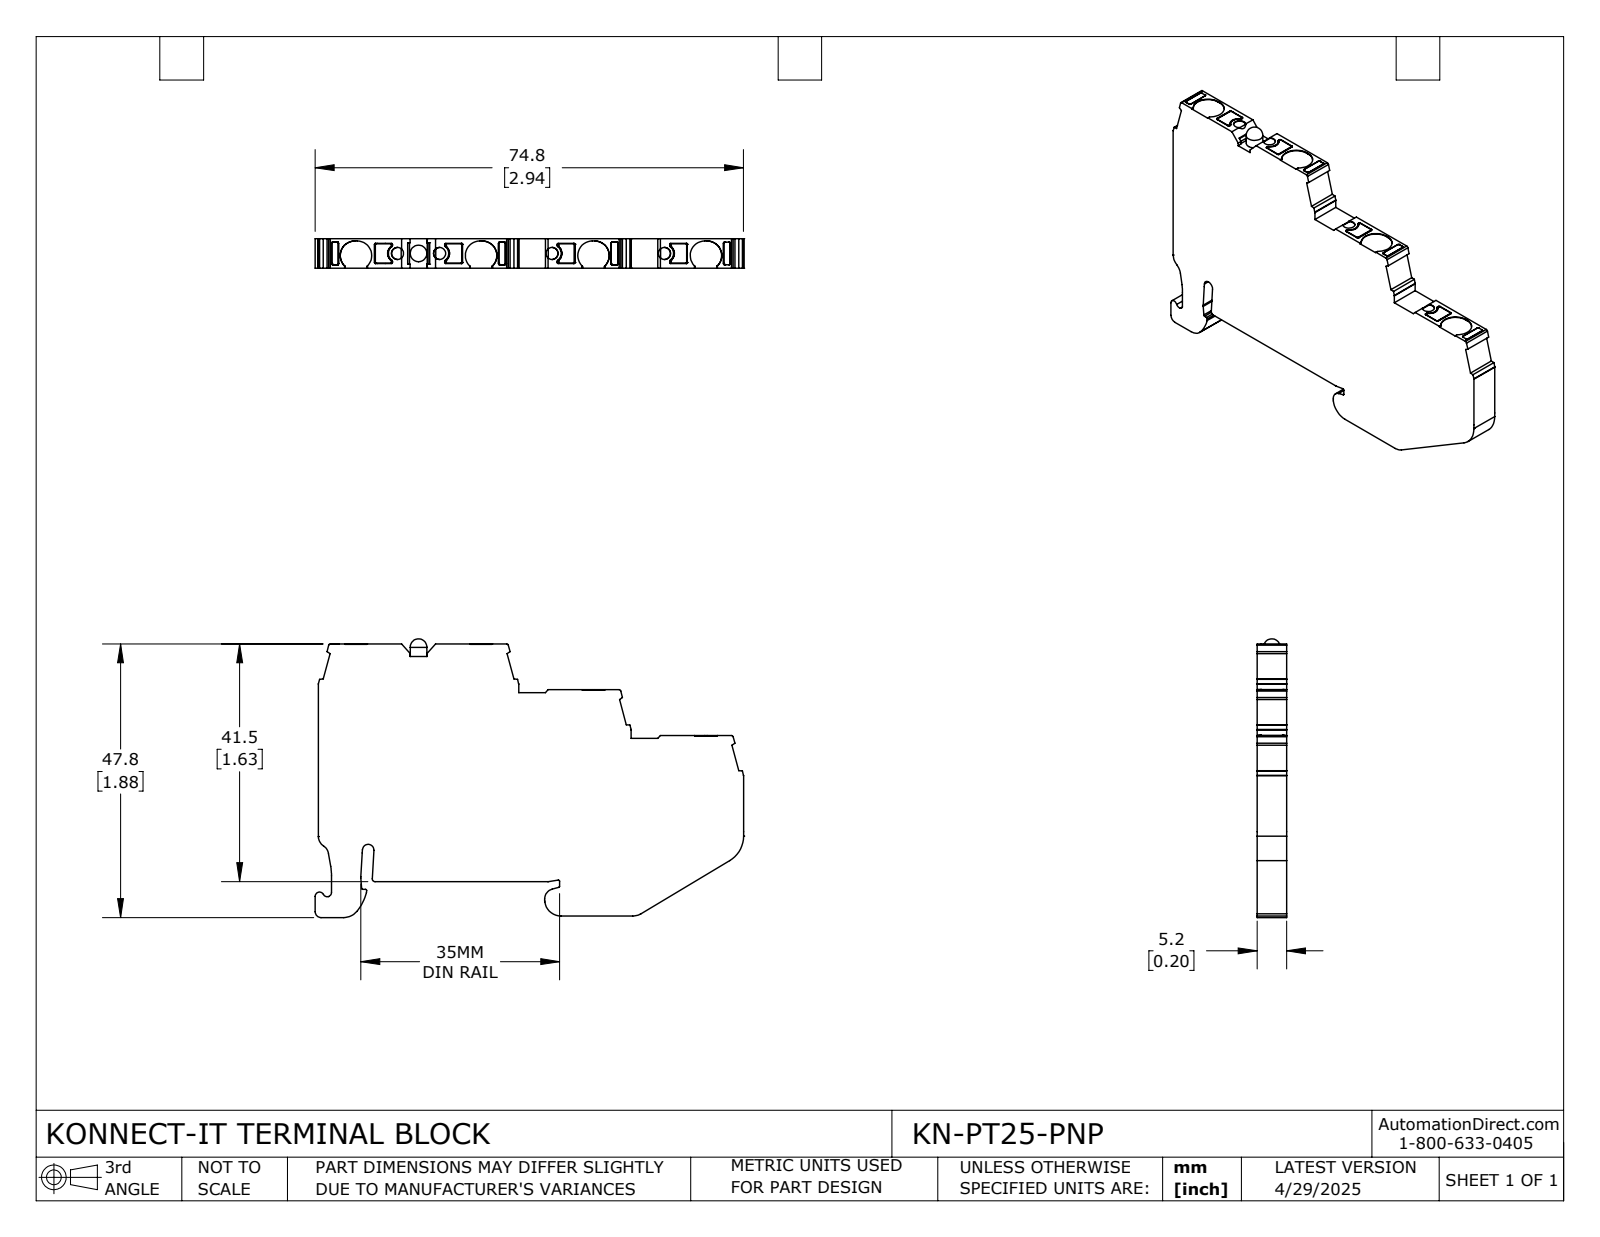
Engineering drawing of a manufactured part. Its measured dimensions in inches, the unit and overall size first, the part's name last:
Units: inches
Overall size (bounding box): 2.945 × 1.915 × 0.203
Round holes (diameter × count): ⌀0.083 ×4
Round bosses / shafts (diameter × count): ⌀0.114 ×1
Partial cylindrical surfaces — rounded edges, fillets, slot ends (radius × count): R0.008 ×68, R0.006 ×16, R0.012 ×8, R0.1 ×8, R0.059 ×4, R0.061 ×4, R0.039 ×3, R0.079 ×3
Main face-to-face distances: 0.203, 0.315, 0.236, 0.63, 0.315, 0.63, 2.923, 0.311, 0.319, 0.016
Hole centre spacings: 0.289, 0.773, 0.773, 1.062, 1.546, 1.835
Volume: 0.841 in³ · Surface area: 10.5 in²
Bodies: 1 solid, 358 faces (201 planar, 146 cylindrical, 11 other)
Part name (STEP PRODUCT): KN-PT25-PNP
STEP written by: SolidWorks 2024 (CONFIG_CONTROL_DESIGN)
